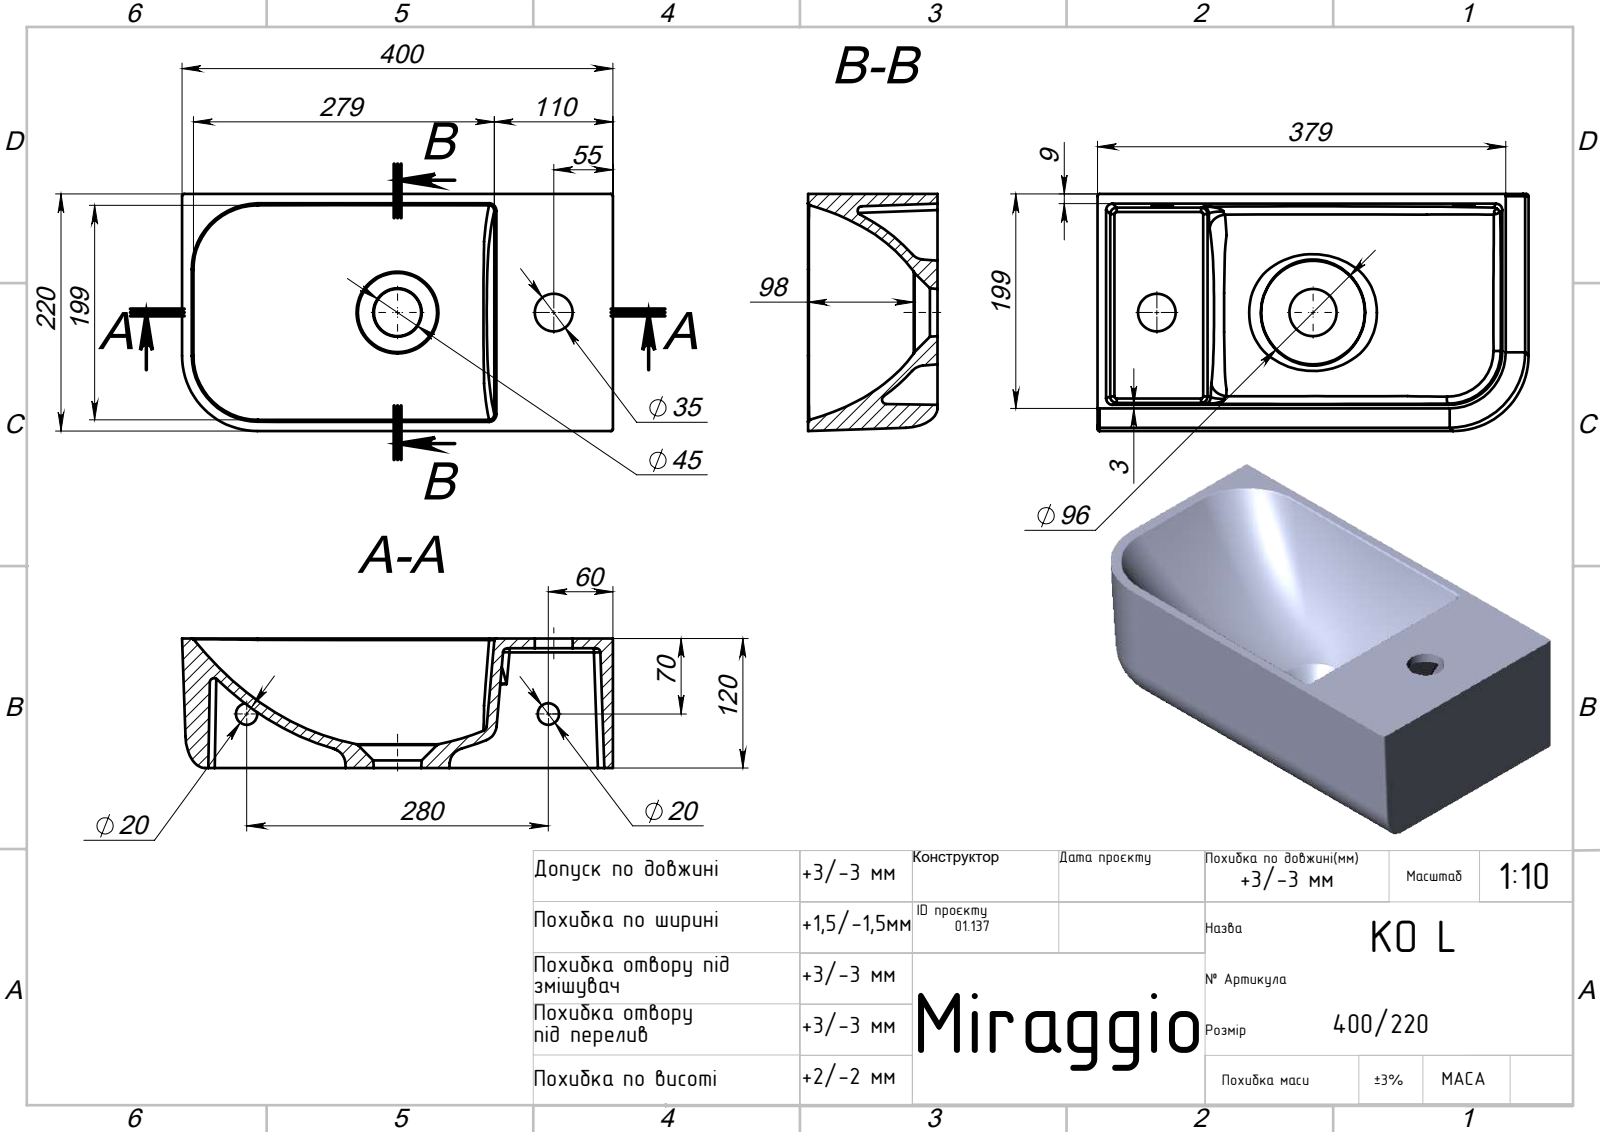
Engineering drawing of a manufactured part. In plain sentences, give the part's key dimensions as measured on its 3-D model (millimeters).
The part is named "Ko L". Its 3-D file was written by "SolidWorks 2020 (AUTOMOTIVE_DESIGN)". It is 1 solid with 68 faces: 17 planar, 17 cylindrical and 34 other. Overall it measures 400 by 220 by 120 millimeters. Its volume is 3 007 000 cubic millimeters and its surface area 460 180 square millimeters. Round holes: 2 of diameter 20, 1 of diameter 35. Partial cylindrical surfaces (rounded edges, fillets, slot ends): 5 of radius 6, 4 of radius 2, 4 of radius 4, 1 of radius 70. The main face-to-face distances are 206.59, 9, 387.41, 111, 120, 378.85, 198.85. The hole center spacings are 280.
